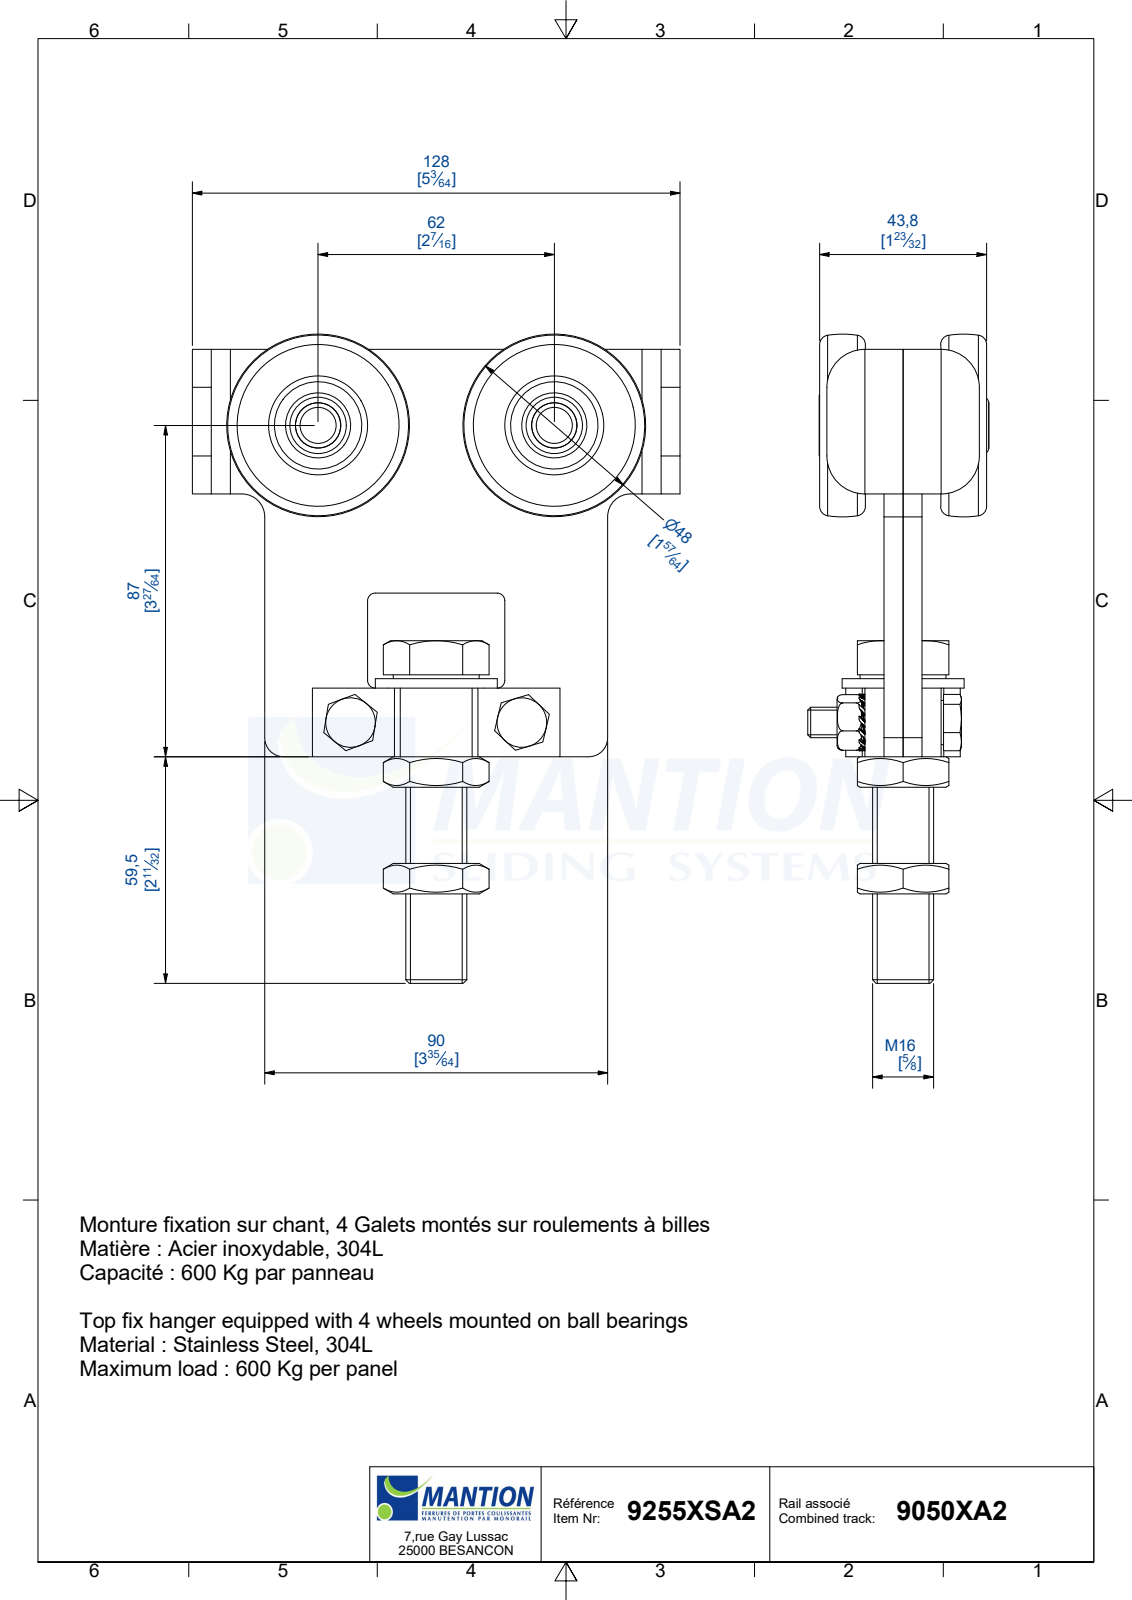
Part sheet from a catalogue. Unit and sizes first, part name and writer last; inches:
Units: inches
Overall size (bounding box): 6.713 × 5.039 × 1.87
Round holes (diameter × count): ⌀0.079 ×8, ⌀0.262 ×2, ⌀0.319 ×2, ⌀0.327 ×2, ⌀0.331 ×2, ⌀0.374 ×2, ⌀0.469 ×2, ⌀0.472 ×2, ⌀0.48 ×2, ⌀0.481 ×2, ⌀0.484 ×2, ⌀0.901 ×2
Round bosses / shafts (diameter × count): ⌀1.26 ×3, ⌀1.157 ×2, ⌀0.709 ×2, ⌀0.674 ×2, ⌀0.63 ×2, ⌀0.487 ×2, ⌀0.458 ×2, ⌀0.315 ×2
Partial cylindrical surfaces — rounded edges, fillets, slot ends (radius × count): R0.014 ×728, R0.071 ×392, R0.05 ×56, R0.295 ×30, R0.079 ×24, R0.23 ×22, R0.394 ×8, R0.197 ×6
Main face-to-face distances: 0.197, 0.394, 0.862, 0.472, 0.39, 0.276, 0.591, 0.665, 1.059, 0.669
Hole centre spacings: 0.484, 0.45, 0.45, 0.739, 3.089, 3.724, 0.24, 0.364
Volume: 14.09 in³ · Surface area: 183.2 in²
Bodies: 34 solids, 2167 faces (282 planar, 1726 cylindrical, 159 other)
Part name (STEP PRODUCT): 9255XSA2; 9852XSPA2; 22250; GALB48XS (+8 more)
STEP written by: Autodesk Inventor 2019 (AUTOMOTIVE_DESIGN)
